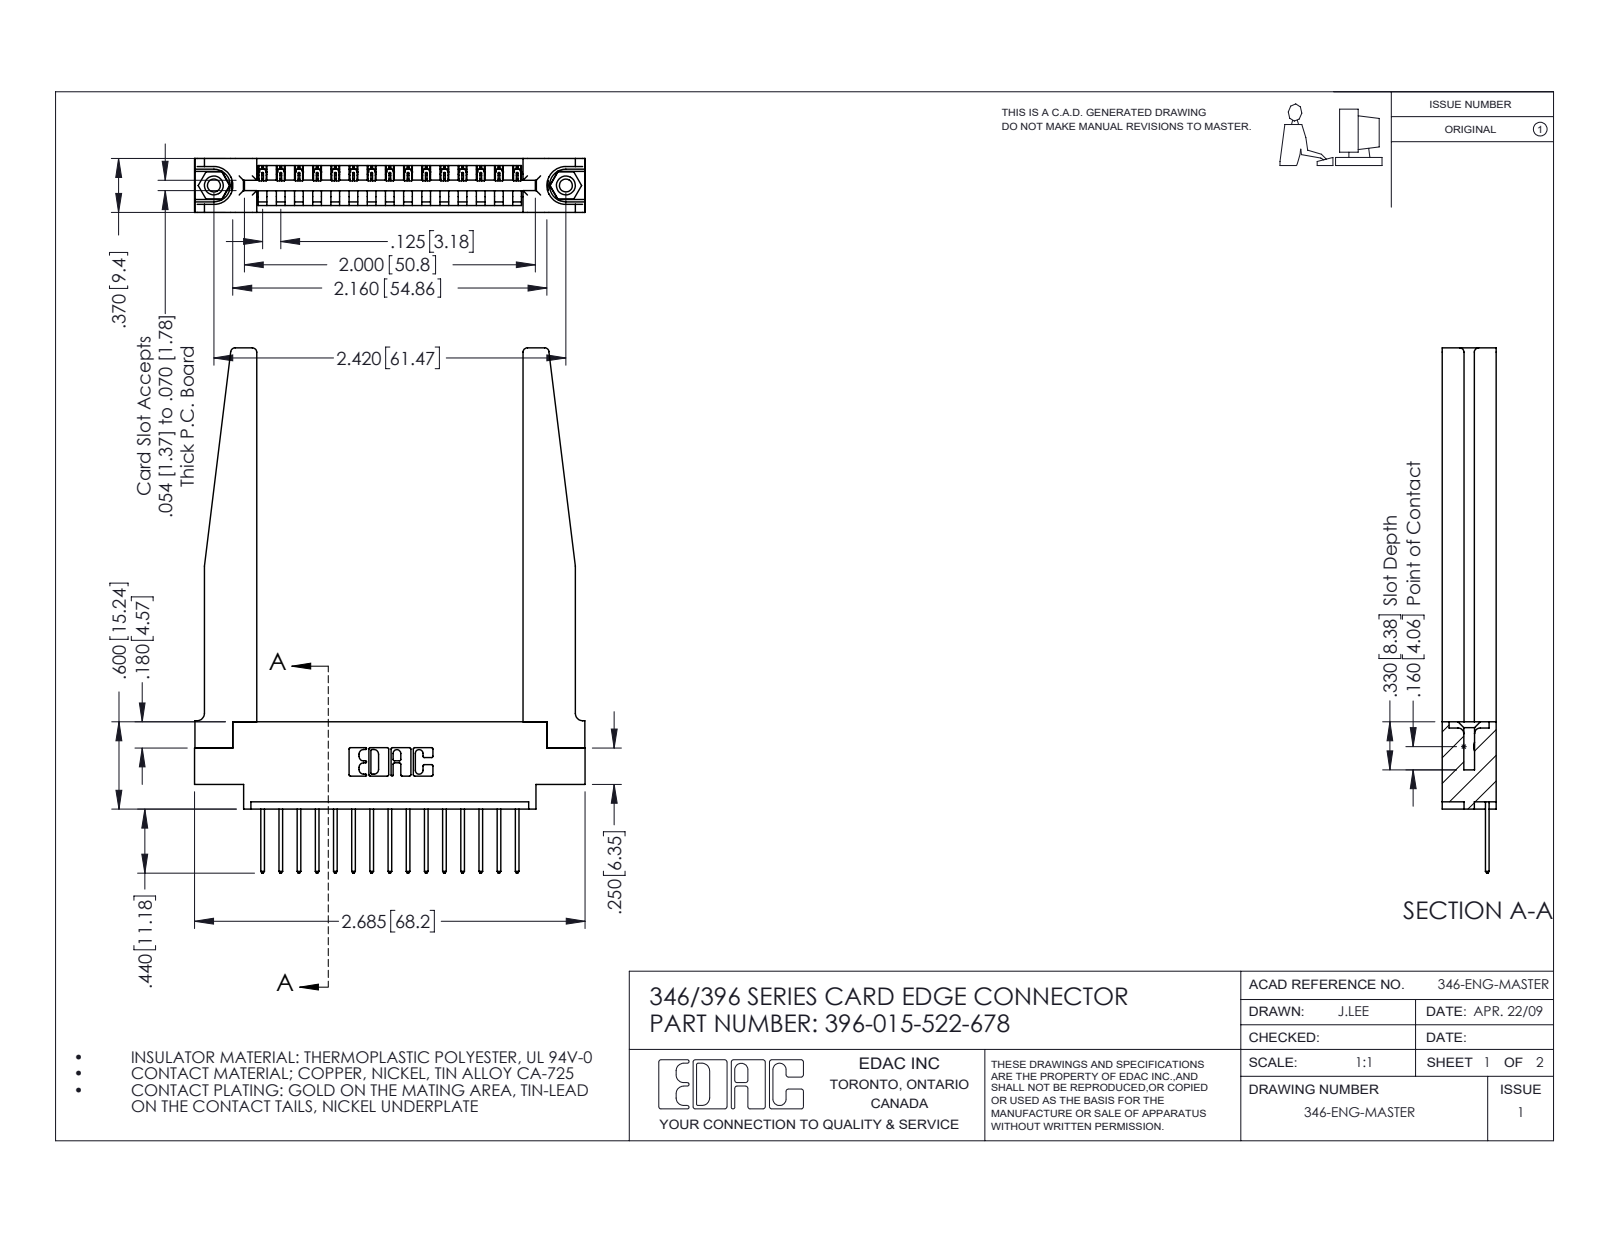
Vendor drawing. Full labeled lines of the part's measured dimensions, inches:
Part name (STEP PRODUCT): 346 Part_0.170 Offset - 0.156 Dia-TH; 396-015-522-678; 346-220-078_345-220-078; 345-250-001_345-250-001-102 (+1 more)
STEP written by: SolidWorks 2016 (CONFIG_CONTROL_DESIGN)
Units: inches
Bodies: 20 solids, 1230 faces (822 planar, 356 cylindrical, 52 other)
Overall size (bounding box): 3.61 × 2.685 × 0.37
Volume: 0.799 in³ · Surface area: 22.01 in²
Round holes (diameter × count): ⌀0.089 ×2, ⌀0.125 ×2, ⌀0.156 ×2, ⌀0.064 ×1
Round bosses / shafts (diameter × count): ⌀0.155 ×2
Partial cylindrical surfaces — rounded edges, fillets, slot ends (radius × count): R0.006 ×30, R0.01 ×30, R0.01 ×22, R0.03 ×8, R0.007 ×6, R0.031 ×6, R0.026 ×3, R0.031 ×2
Main face-to-face distances: 0.37, 0.15, 0.072, 0.048, 0.322, 0.148, 0.25, 0.102, 0.22, 0.173
Hole centre spacings: 0.246, 2.213, 2.42
